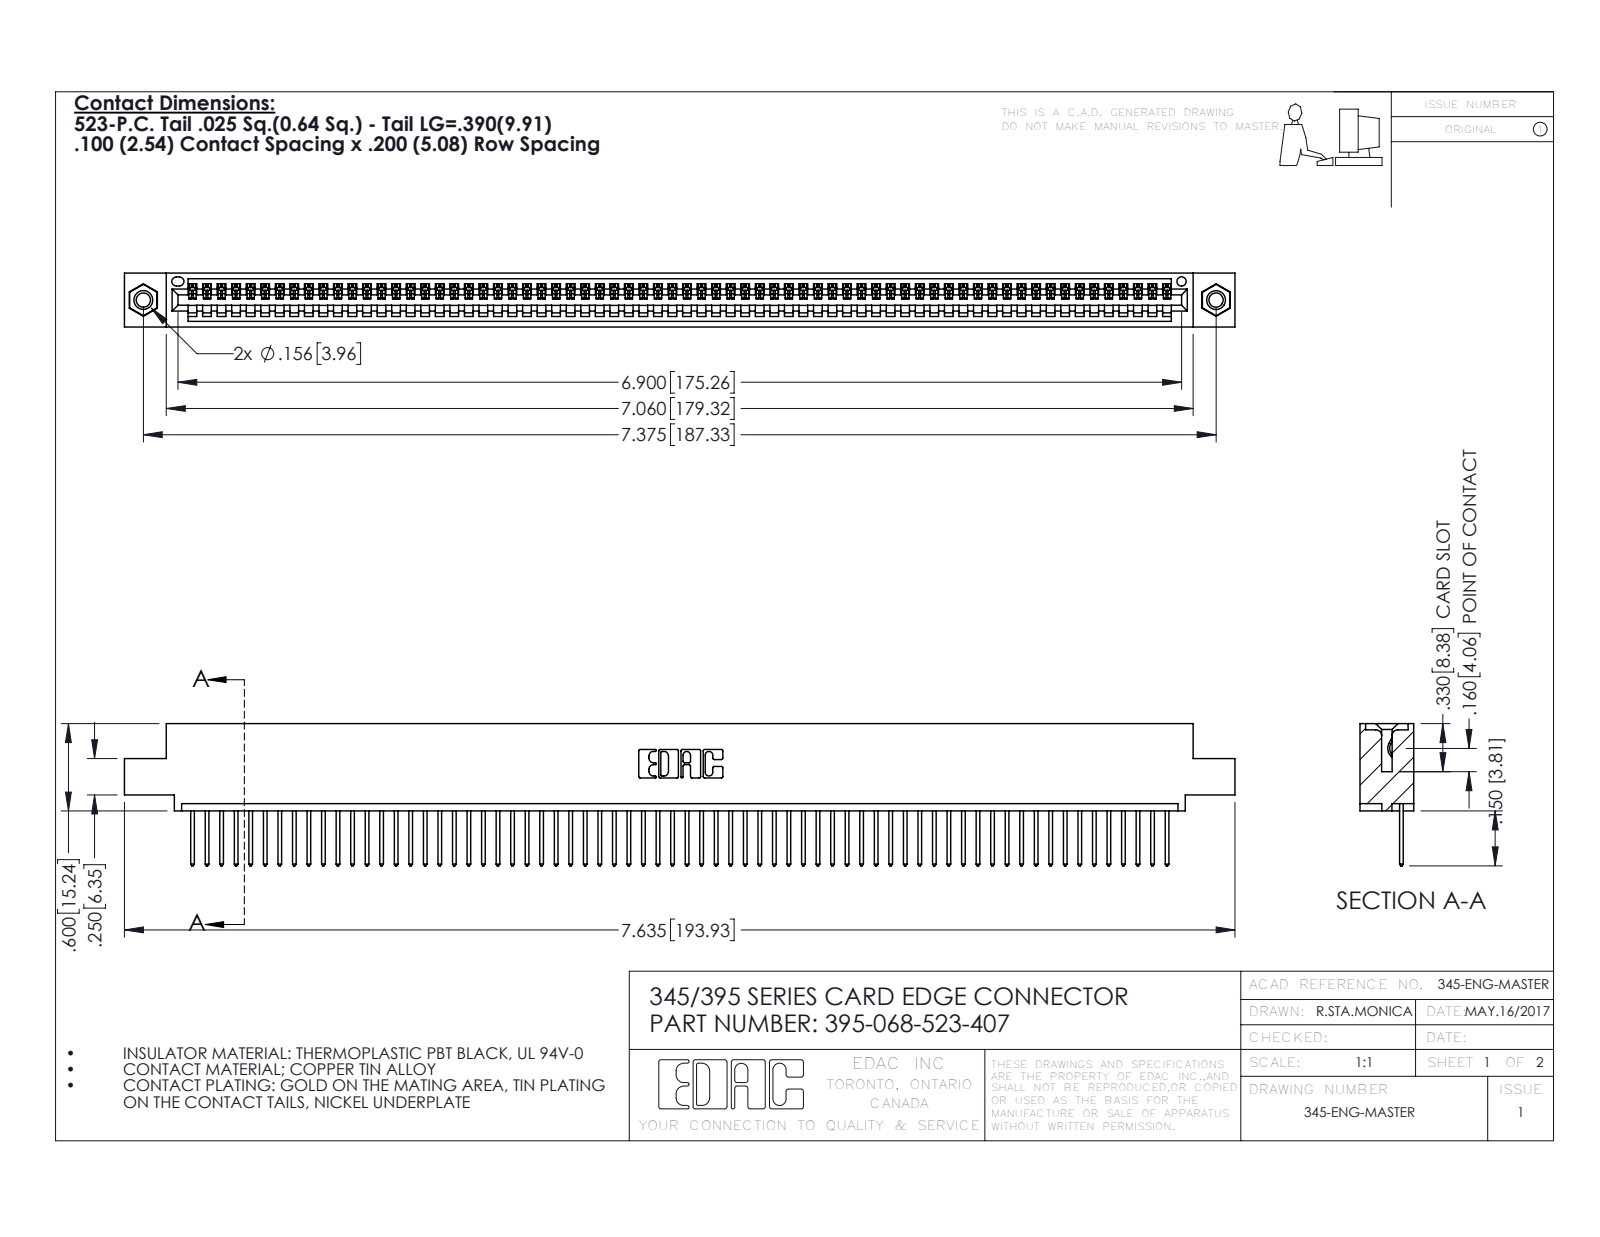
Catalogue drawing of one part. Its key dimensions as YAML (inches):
part_name: "345 Part_0.110 Offset - 0.156 Dia-TI; 345-292-001_345-293-123; 345-250-001_345-250-005-103; 395-068-523-407"
step_written_by: "SolidWorks 2016 (CONFIG_CONTROL_DESIGN)"
units: inches
bodies: {solids: 71, faces: 4134, planar: 2836, cylindrical: 1282, other: 16}
overall_size: [7.635, 0.977, 0.37]
volume: 1.13
surface_area: 38.99
round_holes:
  - {diameter: 0.098, count: 2}
  - {diameter: 0.125, count: 2}
  - {diameter: 0.156, count: 2}
  - {diameter: 0.064, count: 1}
round_bosses_or_shafts:
  - {diameter: 0.155, count: 2}
partial_cylinders:
  - {radius: 0.006, count: 136}
  - {radius: 0.01, count: 136}
  - {radius: 0.01, count: 22}
  - {radius: 0.007, count: 6}
  - {radius: 0.031, count: 6}
  - {radius: 0.026, count: 3}
  - {radius: 0.031, count: 2}
  - {radius: 0.04, count: 2}
face_to_face_distances: [0.072, 0.298, 0.37, 0.098, 0.272, 0.025, 0.2, 0.225, 0.149, 0.072]
hole_center_spacings: [0.27, 7.139, 7.375]
